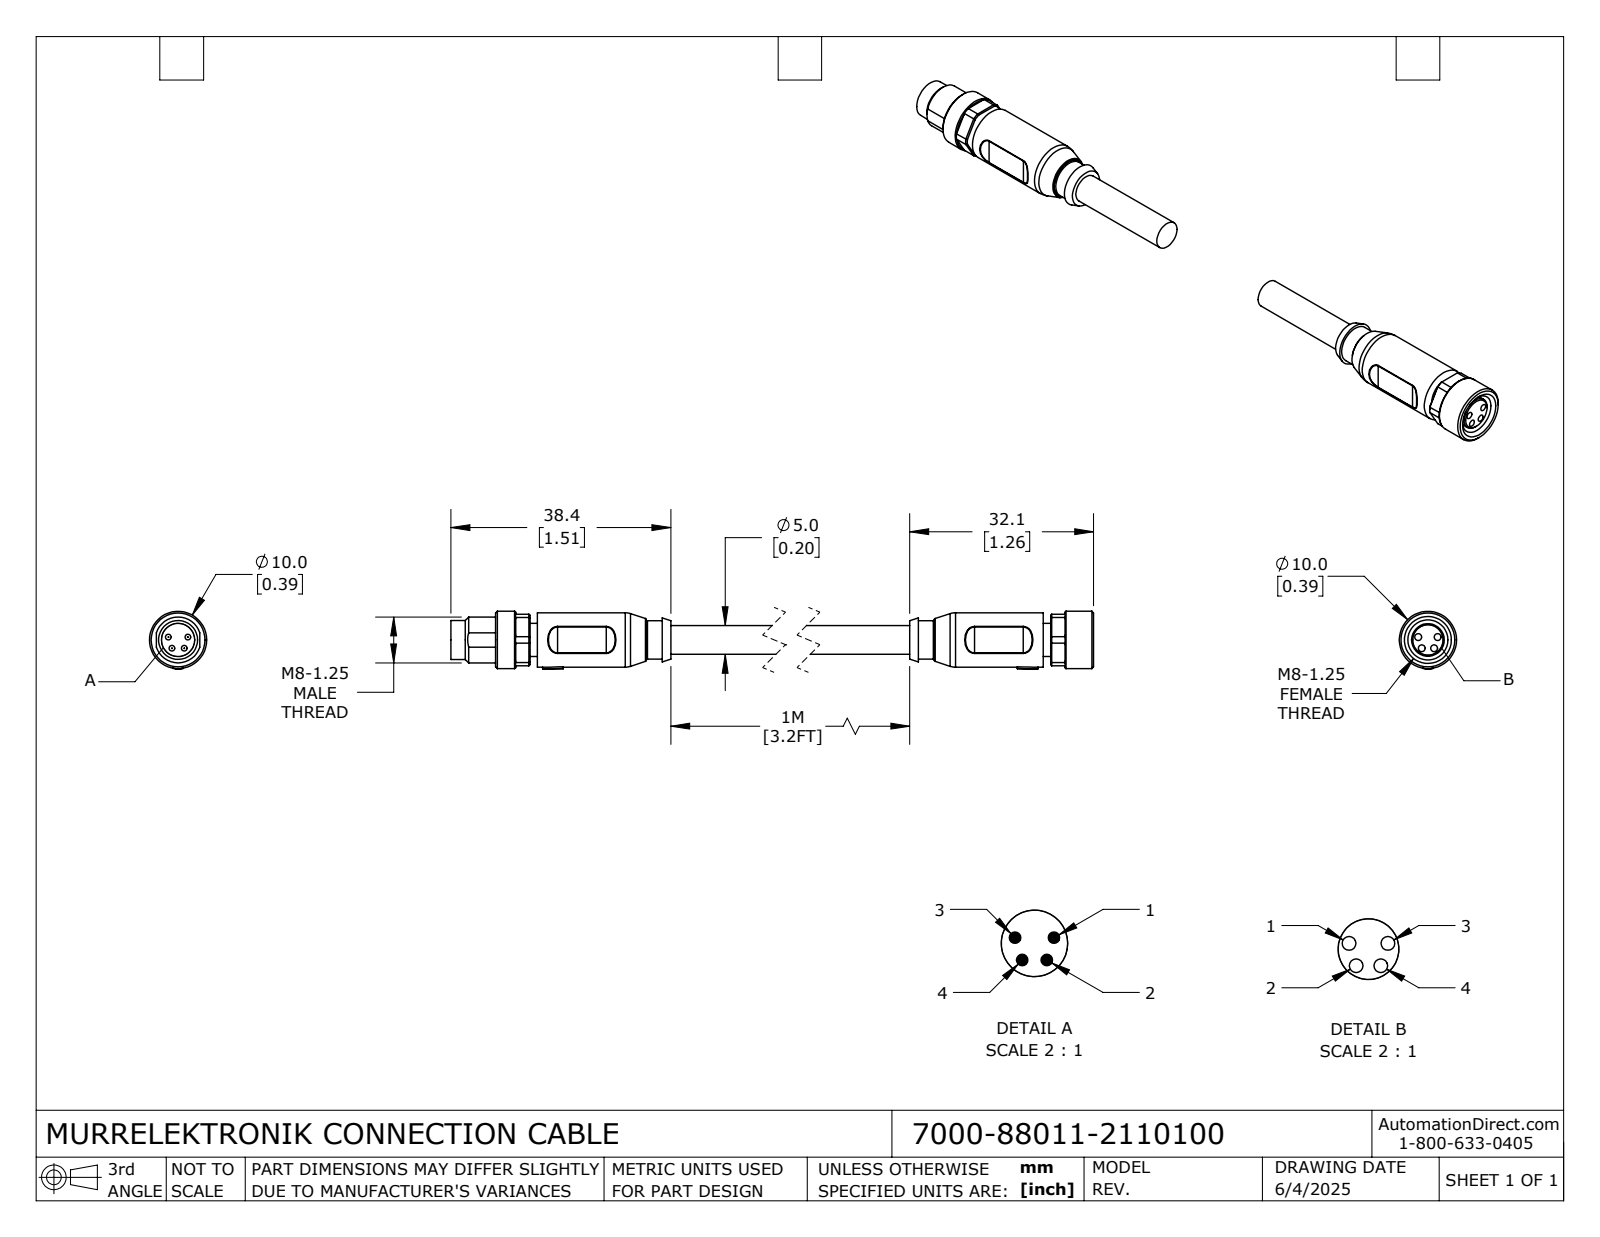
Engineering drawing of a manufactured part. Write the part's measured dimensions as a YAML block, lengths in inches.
part_name: "7000-88011-2110100; 7000-88011-2110100_FEMALE; 7000-88011-2110100_MALE"
step_written_by: "SolidWorks 2024 (CONFIG_CONTROL_DESIGN)"
units: inches
bodies: {solids: 2, faces: 226, planar: 70, cylindrical: 88, other: 68}
overall_size: [5.335, 0.396, 0.394]
volume: 0.294
surface_area: 5.351
round_holes:
  - {diameter: 0.047, count: 4}
  - {diameter: 0.276, count: 1}
round_bosses_or_shafts:
  - {diameter: 0.039, count: 4}
  - {diameter: 0.394, count: 1}
  - {diameter: 0.374, count: 1}
  - {diameter: 0.315, count: 1}
  - {diameter: 0.268, count: 1}
  - {diameter: 0.264, count: 1}
  - {diameter: 0.228, count: 1}
  - {diameter: 0.224, count: 1}
partial_cylinders:
  - {radius: 0.098, count: 8}
  - {radius: 0.008, count: 4}
  - {radius: 0.193, count: 1}
  - {radius: 0.199, count: 1}
face_to_face_distances: [0.327, 0.051, 4.445, 0.354, 4.791, 4.394, 0.969, 0.346, 1.756, 2.74]
hole_center_spacings: [0.07, 0.081, 0.134, 0.071, 0.071, 0.085, 0.133]
